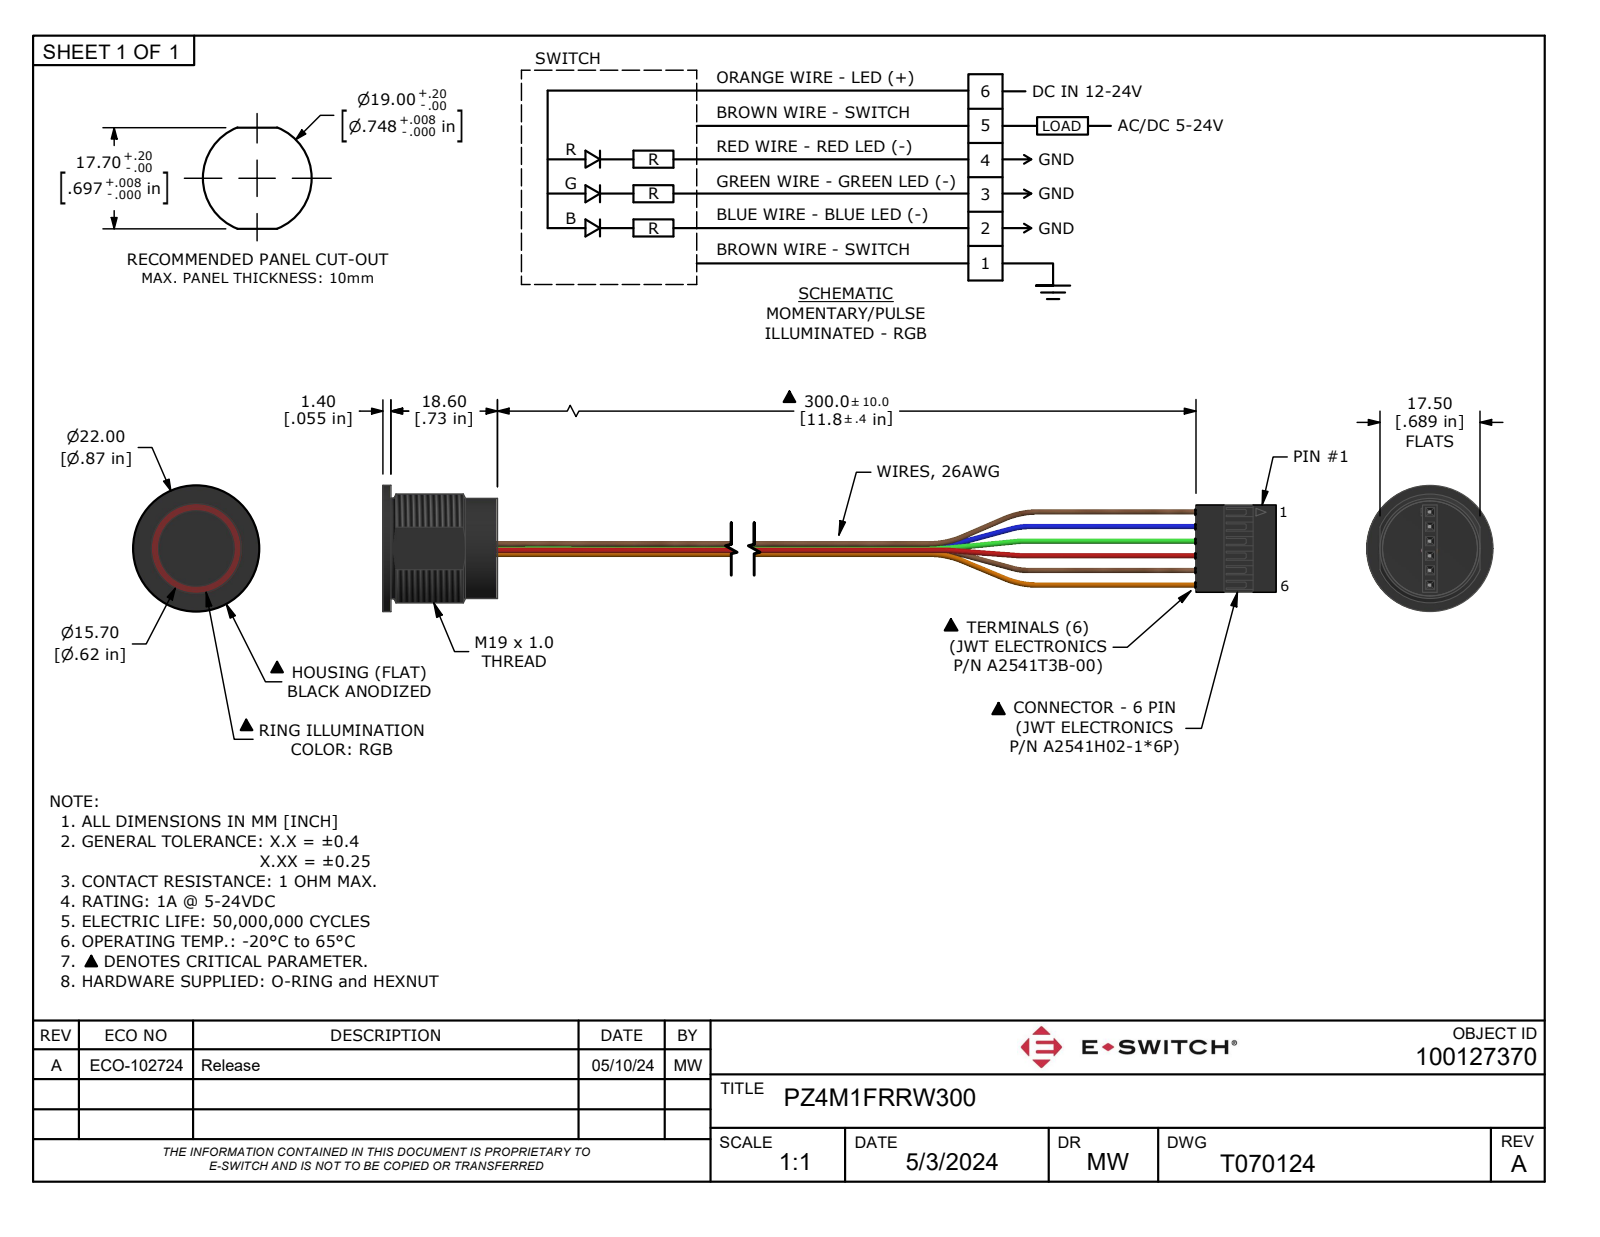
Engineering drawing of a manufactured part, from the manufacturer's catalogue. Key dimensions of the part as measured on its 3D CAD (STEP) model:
STEP written by: Autodesk Inventor 2022 (AUTOMOTIVE_DESIGN)
Units: inches
Bodies: 5 solids, 214 faces (144 planar, 46 cylindrical, 24 other)
Overall size (bounding box): 13.15 × 0.866 × 0.866
Volume: 0.438 in³ · Surface area: 13.7 in²
Round holes (diameter × count): ⌀0.618 ×1
Round bosses / shafts (diameter × count): ⌀0.039 ×16, ⌀0.028 ×6, ⌀0.866 ×1, ⌀0.693 ×1, ⌀0.689 ×1, ⌀0.52 ×1
Partial cylindrical surfaces — rounded edges, fillets, slot ends (radius × count): R0.01 ×12, R0.374 ×1
Main face-to-face distances: 0.1, 0.019, 0.081, 0.055, 0.294, 0.394, 0.063, 0.376, 0.313, 0.2
